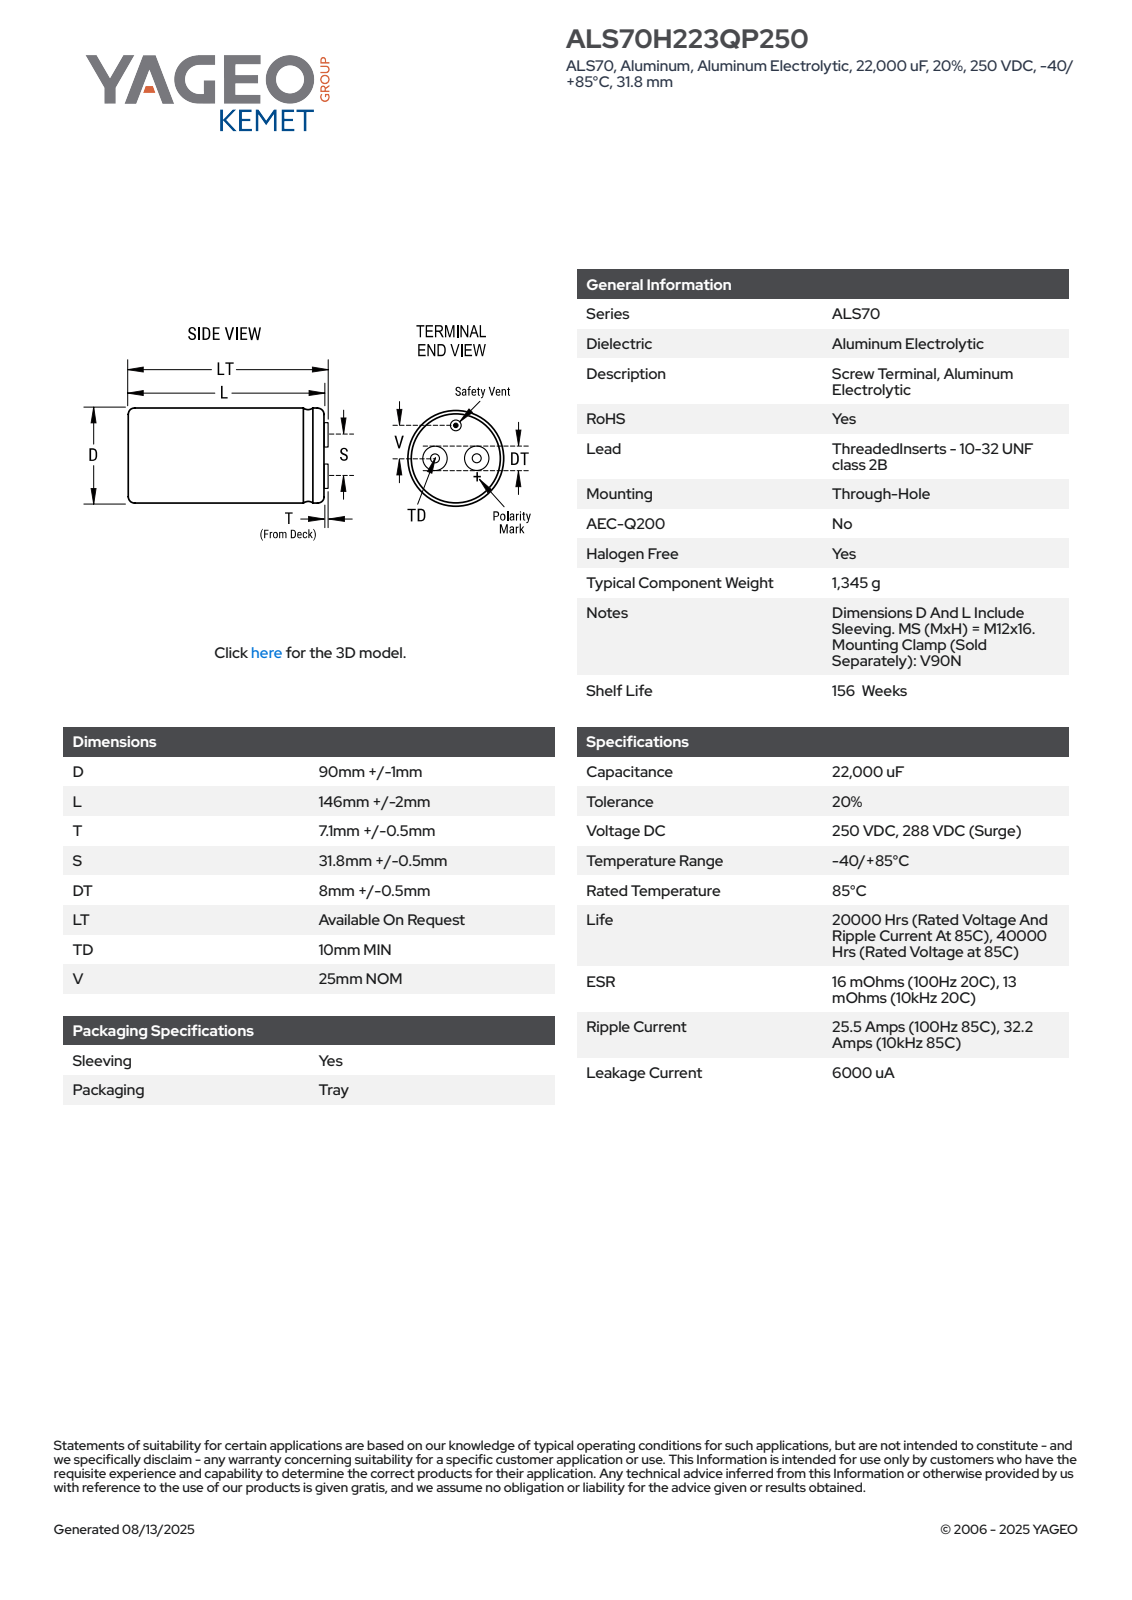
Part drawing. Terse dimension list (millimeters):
name: CARC_KAR_90X146_D91L148T7.6S31.8DT8.500TD10.000V25.000
written by: SolidWorks 2014 (AUTOMOTIVE_DESIGN)
unit: mm
bodies: 1 solid, 88 faces (30 planar, 19 cylindrical, 39 other)
size: 155.6 × 91.01 × 91
volume: 958 572 mm³; area: 55 855 mm²
holes: 2× ⌀5, 1× ⌀1.33
bosses: 2× ⌀8.5, 1× ⌀91, 1× ⌀2.27
rounds: 1× R45.51
face distances: 148, 155.6, 7.6, 145.6, 2.4, 10, 148.35, 2.75, 0.35, 7.25
hole spacings: 29.63, 31.8
